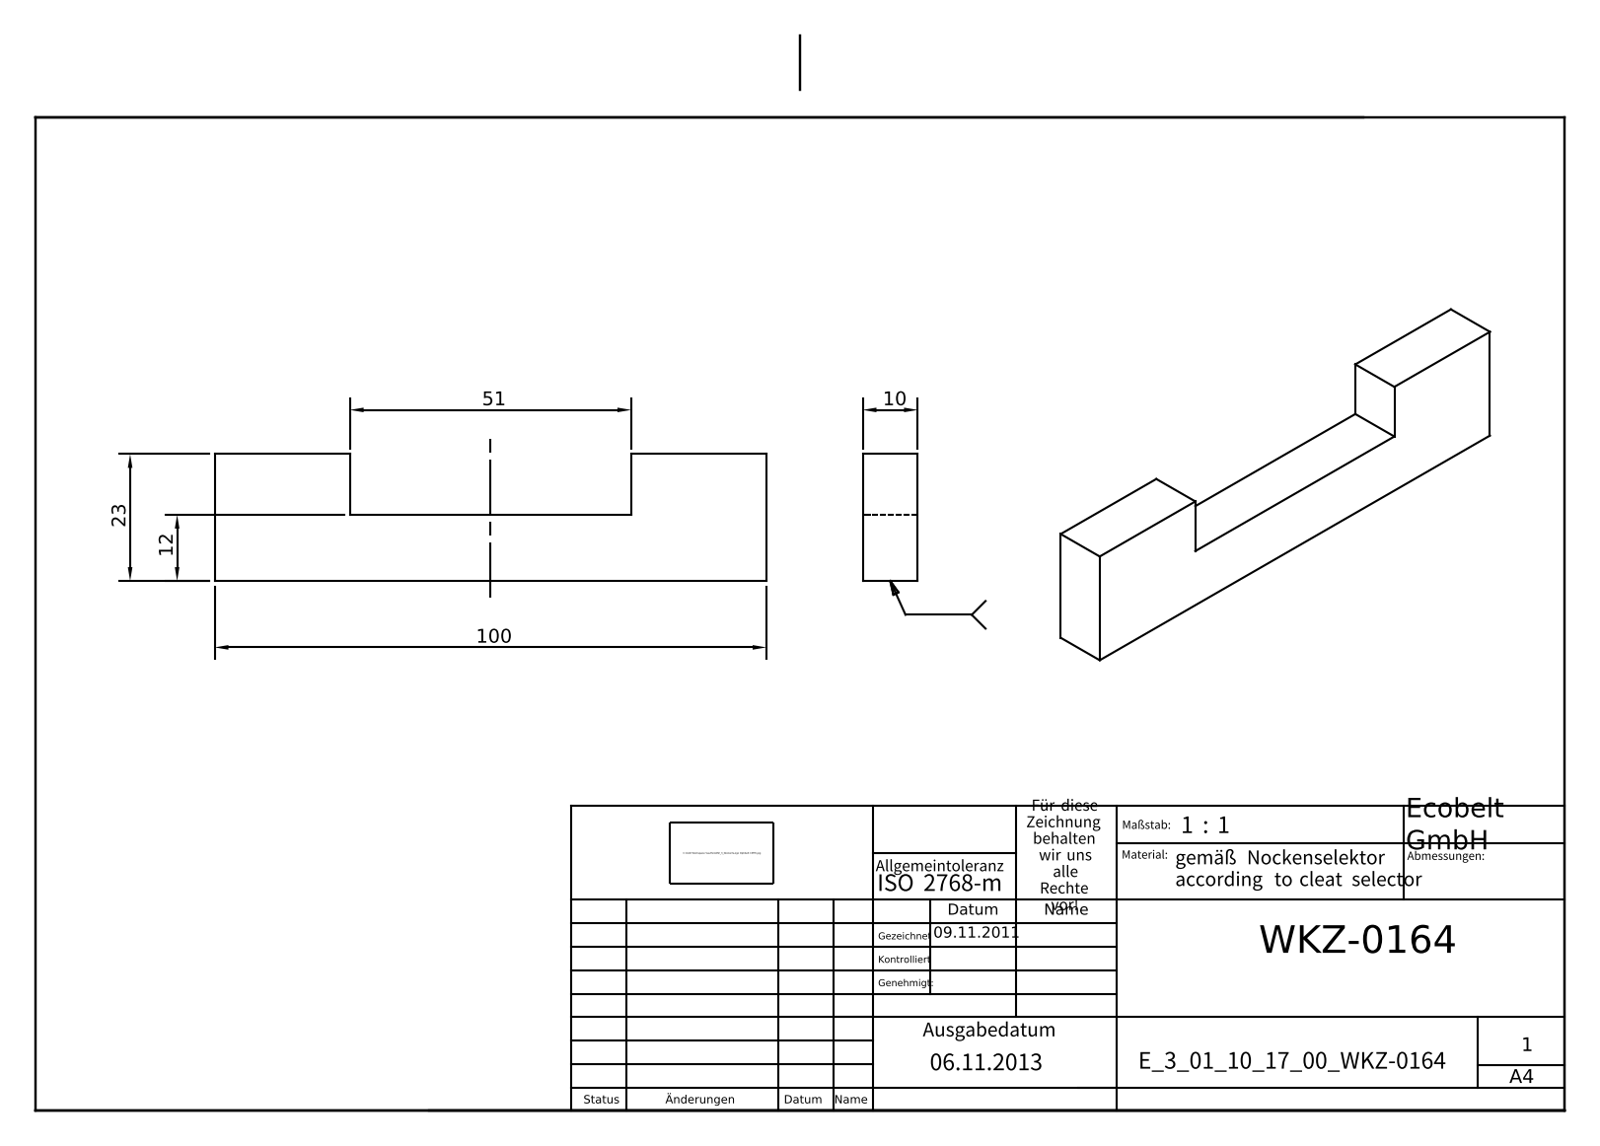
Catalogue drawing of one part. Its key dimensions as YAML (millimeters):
part_name: "E_3_01_10_17_00_WKZ-0164"
step_written_by: "Autodesk Inventor 2025 (AUTOMOTIVE_DESIGN)"
units: millimeters
bodies: {solids: 1, faces: 10, planar: 10, cylindrical: 0, other: 0}
overall_size: [100, 23, 10]
volume: 17390
surface_area: 6158
face_to_face_distances: [10, 12, 23, 11, 100, 24.5, 75.5, 51]
